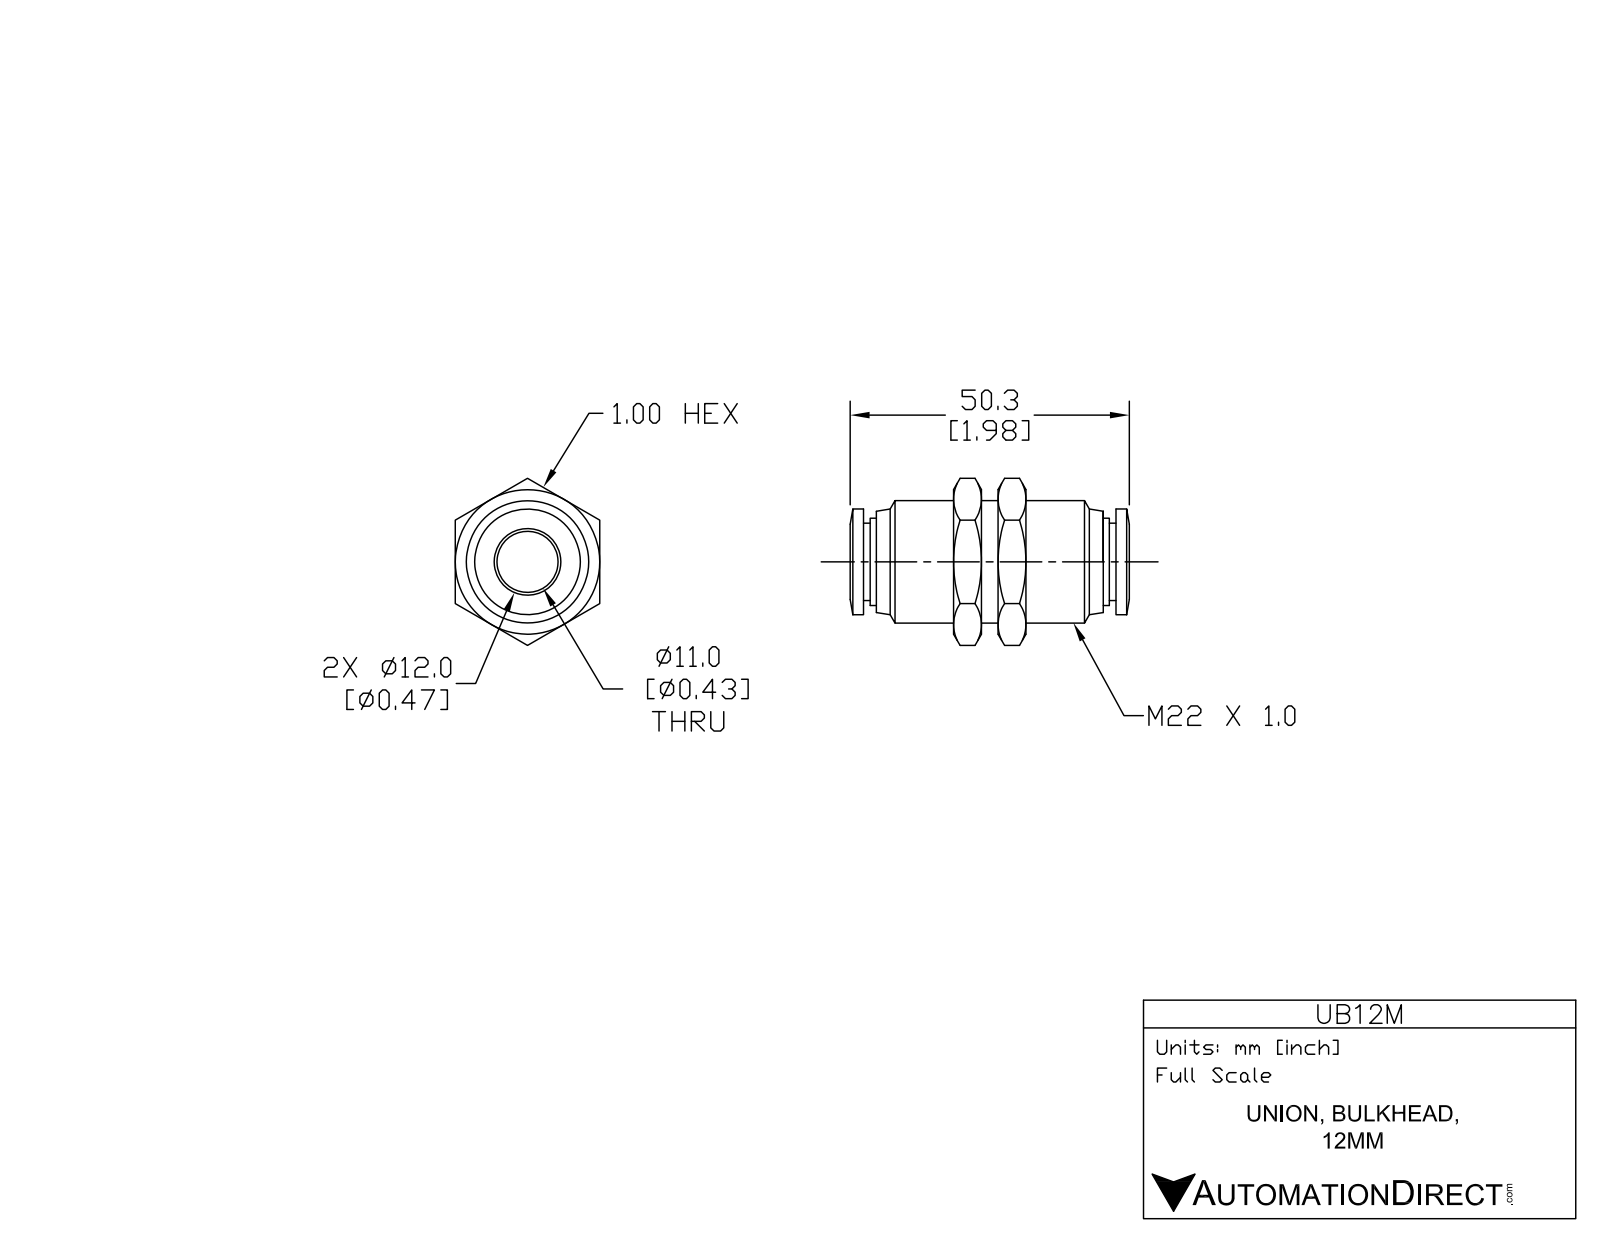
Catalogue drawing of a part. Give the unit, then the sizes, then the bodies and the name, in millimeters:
Units: millimetres
Overall size (bounding box): 50.2 × 30 × 26
Round holes (diameter × count): ⌀11 ×1, ⌀12.3 ×1
Round bosses / shafts (diameter × count): ⌀22 ×1, ⌀19 ×1, ⌀15.4 ×1, ⌀13.9 ×1
Main face-to-face distances: 26, 8, 5, 16.2, 21.2, 24.2, 29.2, 21.9, 3, 13
Volume: 13 100 mm³ · Surface area: 7 000 mm²
Bodies: 1 solid, 94 faces (26 planar, 24 cylindrical, 44 other)
Part name (STEP PRODUCT): UB12M
STEP written by: SolidWorks 2015 (AUTOMOTIVE_DESIGN)
